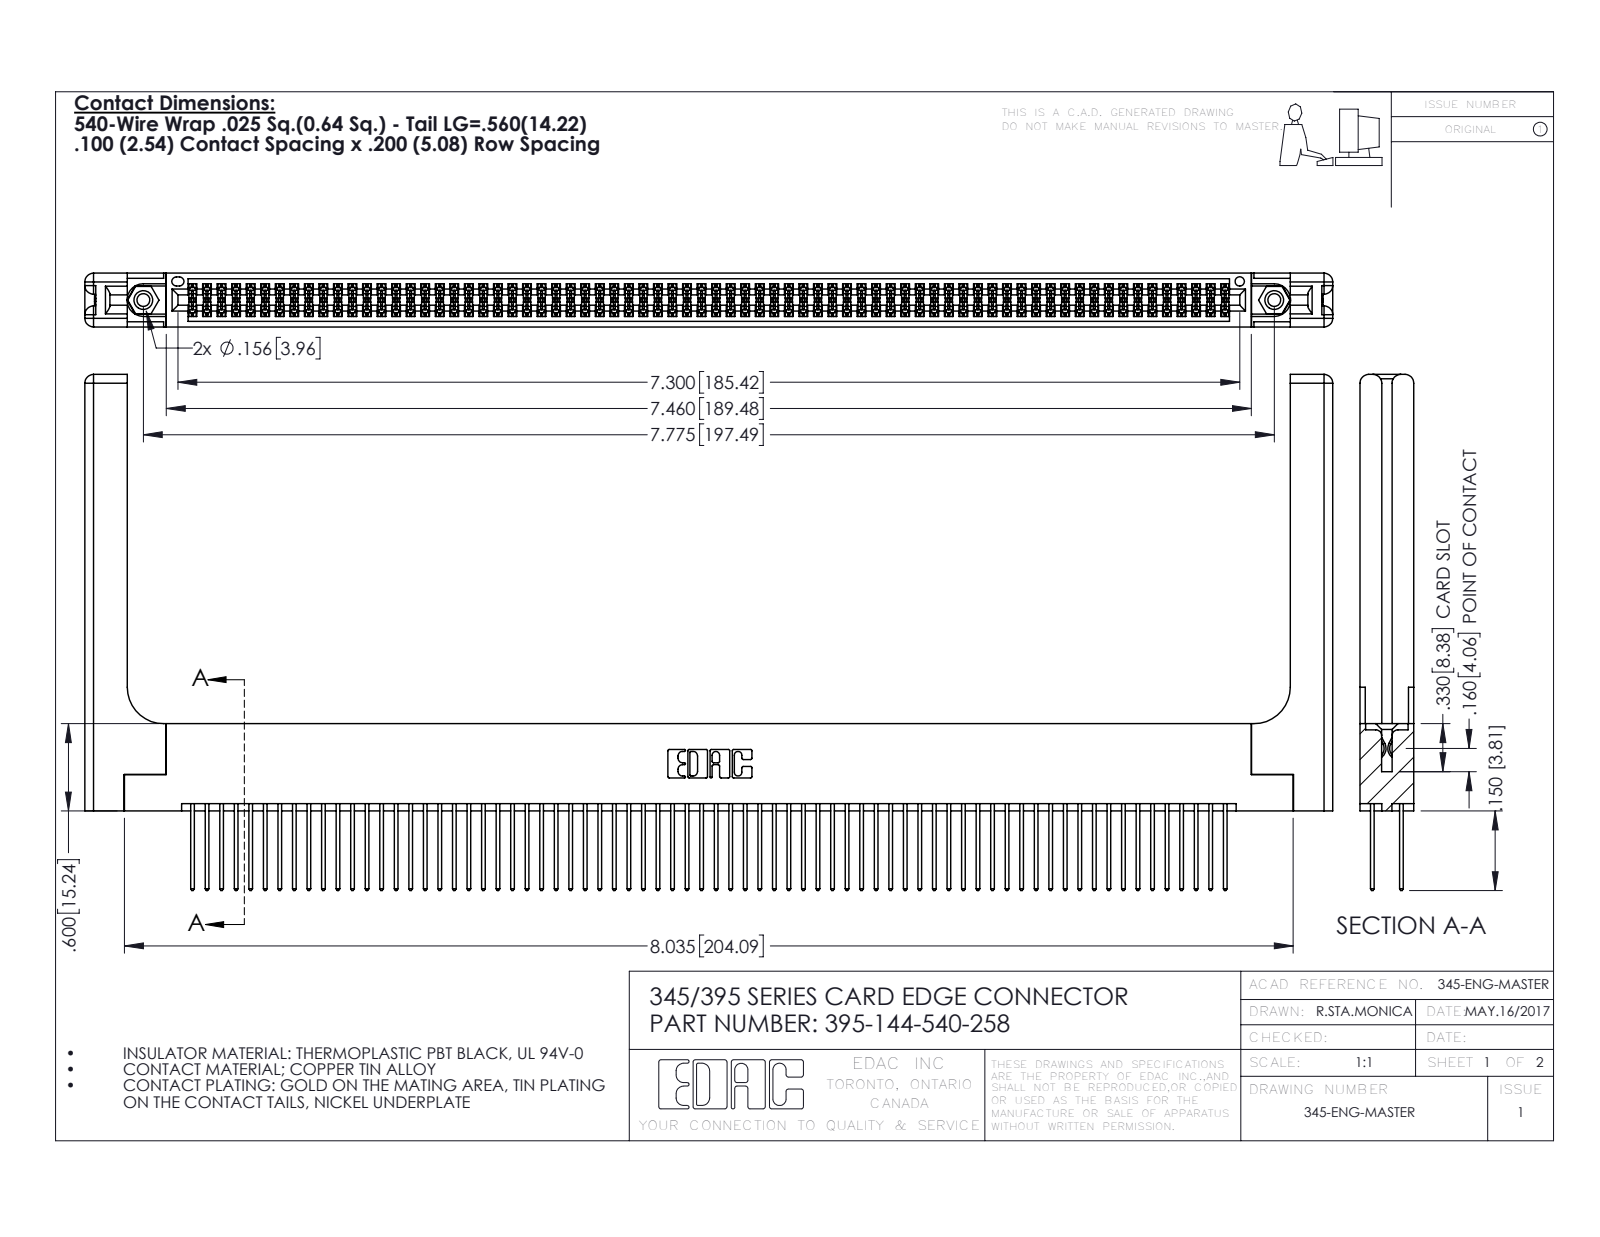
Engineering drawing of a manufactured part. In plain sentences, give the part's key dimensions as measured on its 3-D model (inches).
The part is named "345-220-058_345-220-058; 345-250-001_345-250-001-102; 345 Part_Flush Mounting Lugs - 0.156 Dia-TH; 395-144-540-258 (+1 more)". Its 3-D file was written by "SolidWorks 2016 (CONFIG_CONTROL_DESIGN)". It is 149 solids with 7582 faces: 4980 planar, 2542 cylindrical and 60 other. Overall it measures 8.579 by 3.547 by 0.37 inches. Its volume is 1.859 cubic inches and its surface area 63.05 square inches. Round holes: 2 of diameter 0.089, 2 of diameter 0.125, 2 of diameter 0.156, 1 of diameter 0.064. Round bosses or shafts: 2 of diameter 0.155. Partial cylindrical surfaces (rounded edges, fillets, slot ends): 216 of radius 0.006, 144 of radius 0.01, 22 of radius 0.01, 16 of radius 0.06, 6 of radius 0.007, 6 of radius 0.031, 3 of radius 0.026, 2 of radius 0.014. The main face-to-face distances are 0.072, 0.298, 0.2, 0.37, 0.098, 0.272, 0.025, 0.225, 0.175, 0.148. The hole center spacings are 0.27, 7.539, 7.775.
